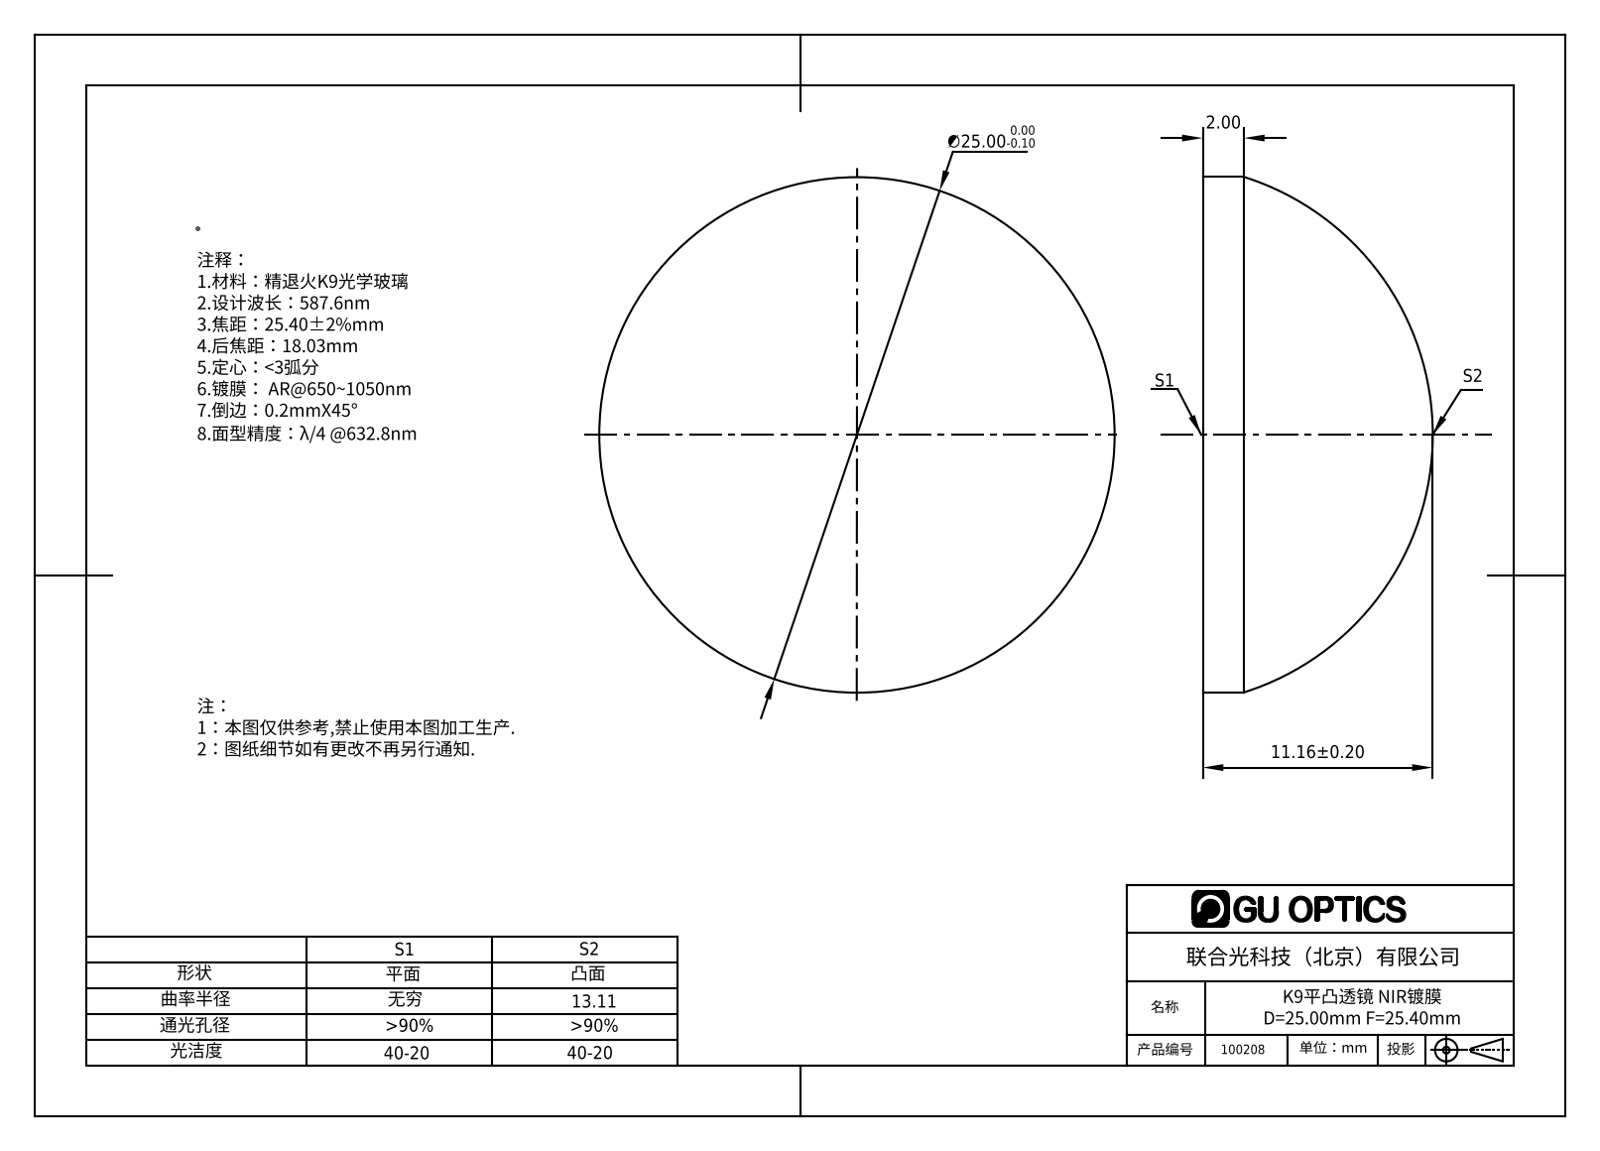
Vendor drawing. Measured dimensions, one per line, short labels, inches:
name: 100208
written by: SolidWorks 2016 (AUTOMOTIVE_DESIGN)
unit: in
bodies: 1 solid, 5 faces (1 planar, 2 cylindrical, 2 other)
size: 0.984 × 0.984 × 0.439
volume: 0.222 in³; area: 2.173 in²
bosses: 1× ⌀0.984
